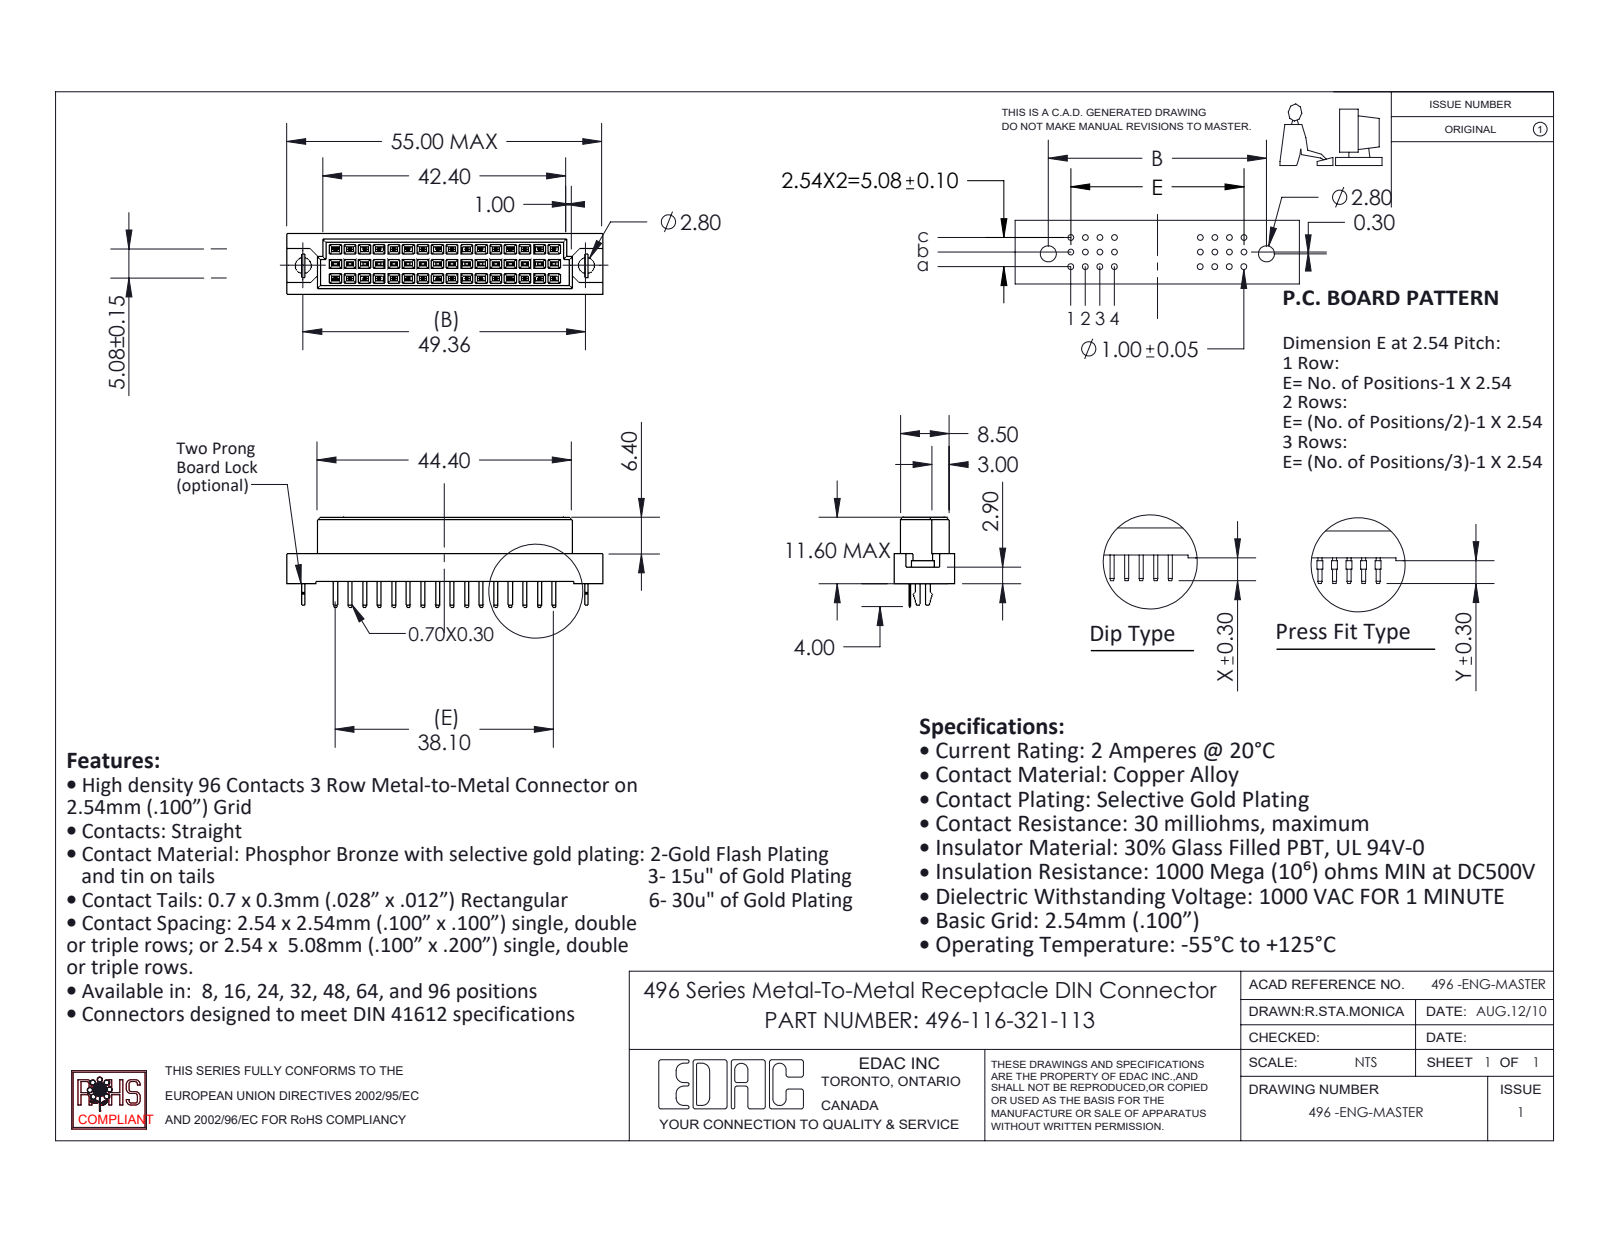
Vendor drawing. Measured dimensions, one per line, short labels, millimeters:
name: 496 Bore-lock; 496-290_21; 496 Part_48; 496-116-321-113
written by: SolidWorks 2020 (CONFIG_CONTROL_DESIGN)
unit: mm
bodies: 19 solids, 862 faces (856 planar, 6 cylindrical, 0 other)
size: 55 × 15.6 × 10.6
volume: 4 640 mm³; area: 4 601 mm²
holes: 2× ⌀2.8
rounds: 1× R0.53
face distances: 2.54, 1.05, 9.55, 5.08, 0.81, 10.6, 3.35, 1.73, 8.5, 0.56
hole spacings: 49.36
